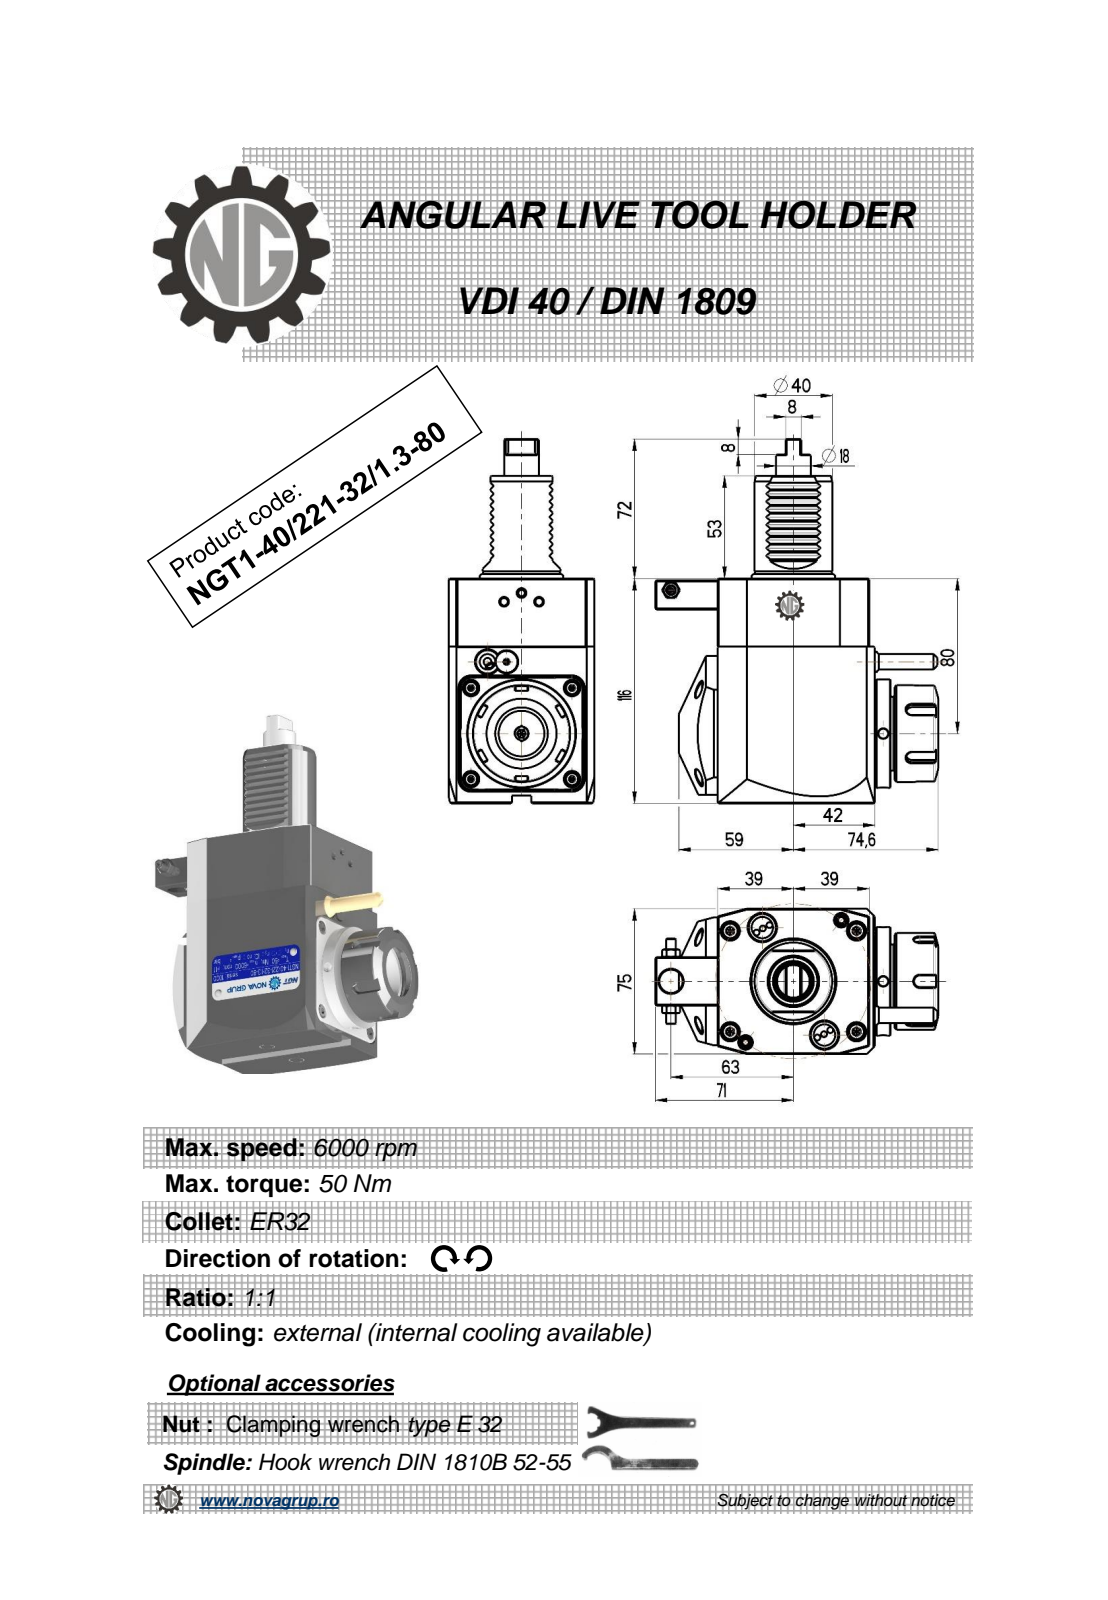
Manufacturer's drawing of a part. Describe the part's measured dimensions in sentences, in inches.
The part is named "NGT1_40_221_32_1_3_80". Its 3-D file was written by "PRO/ENGINEER BY PARAMETRIC TECHNOLOGY CORPORATION, 2010280 (CONFIG_CONTROL_DESIGN)". It is 1 solid with 459 faces: 228 planar, 94 cylindrical and 137 other. Overall it measures 7.402 by 5.732 by 2.953 inches. Its volume is 53.17 cubic inches and its surface area 110.1 square inches. Round holes: 3 of diameter 0.197, 1 of diameter 0.118, 1 of diameter 0.165, 1 of diameter 0.374, 1 of diameter 0.472, 1 of diameter 1.063. Round bosses or shafts: 1 of diameter 2.205, 1 of diameter 1.969, 1 of diameter 1.693, 1 of diameter 1.575, 1 of diameter 0.701, 1 of diameter 0.441, 1 of diameter 0.353, 1 of diameter 0.315. Partial cylindrical surfaces (rounded edges, fillets, slot ends): 20 of radius 0.012, 12 of radius 0.01, 6 of radius 0.009, 5 of radius 0.118, 2 of radius 0.031, 1 of radius 1.575. The main face-to-face distances are 2.953, 4.567, 3.189, 3.071, 0.118, 3.181, 0.11, 0.295, 0.433, 0.02. The hole center spacings are 1.558, 1.611, 2.854, 4.301, 5.195.
